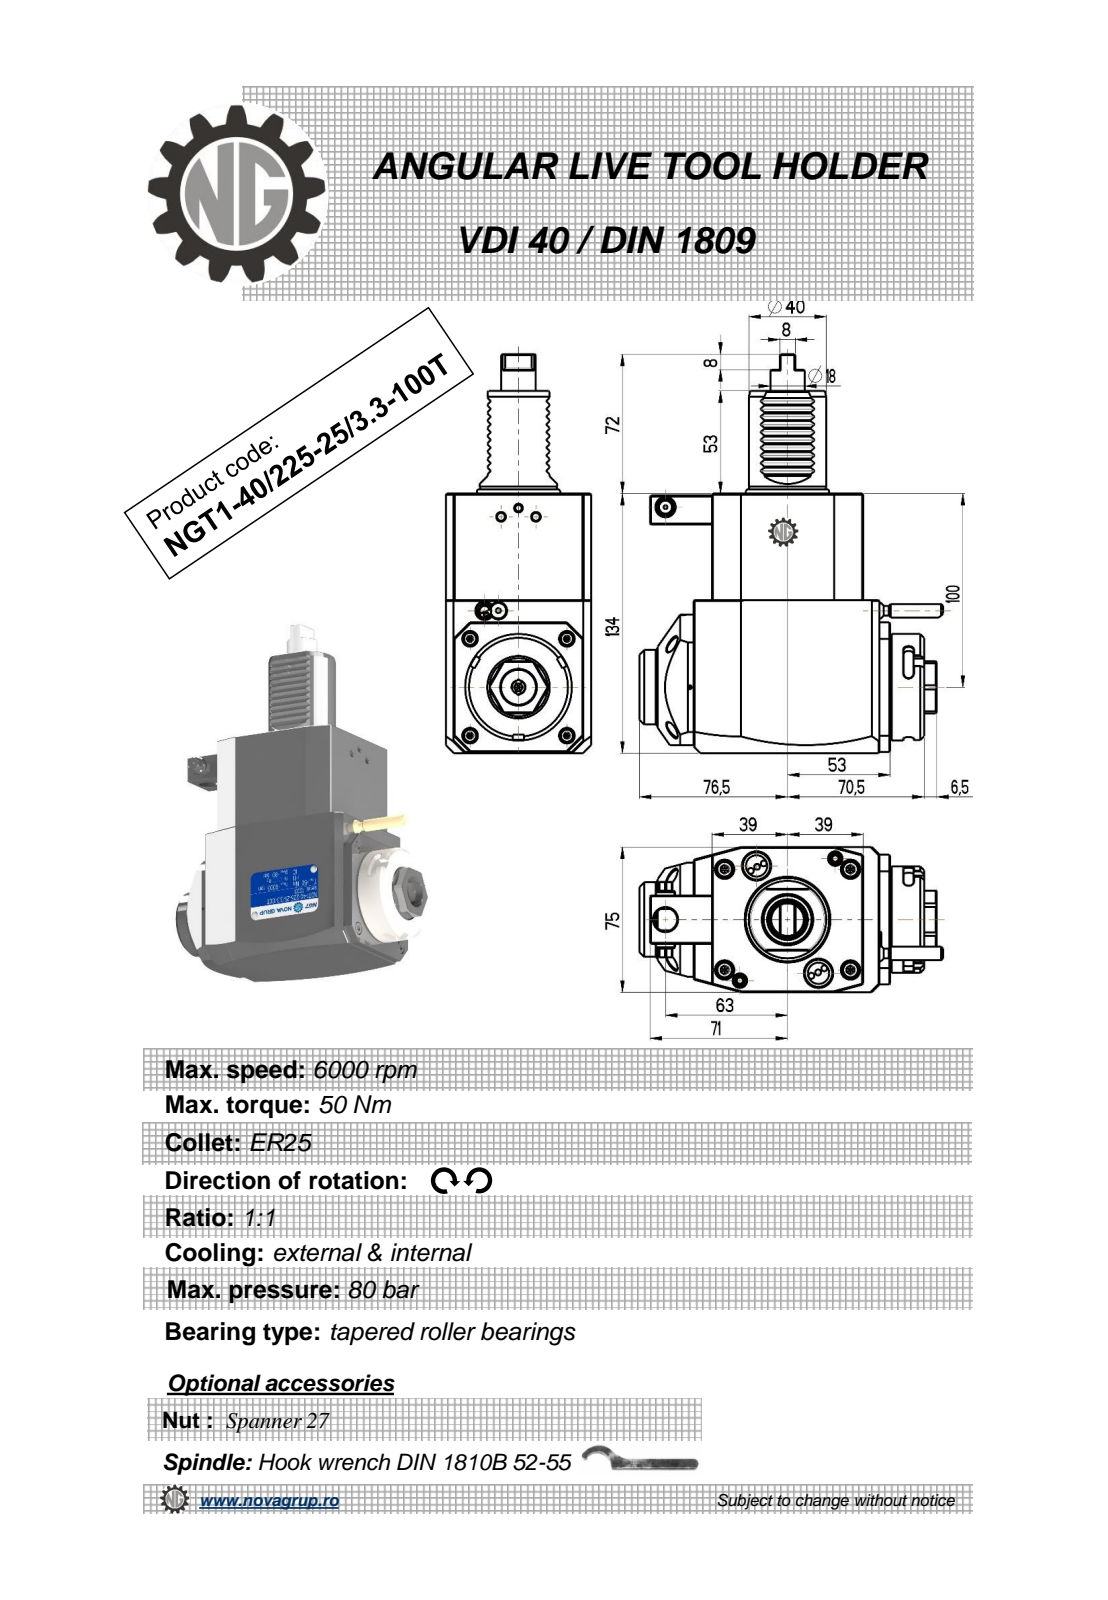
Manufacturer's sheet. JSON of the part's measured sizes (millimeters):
{"part_name": "NGT1_40_225_25_3_3_100T", "step_written_by": "PRO/ENGINEER BY PARAMETRIC TECHNOLOGY CORPORATION, 2010280 (CONFIG_CONTROL_DESIGN)", "units": "millimeters", "bodies": {"solids": 1, "faces": 392, "planar": 217, "cylindrical": 97, "other": 78}, "overall_size": [206, 156.83, 75], "volume_mm3": 1071000, "surface_area_mm2": 77452, "round_holes": [[2, 1], [2.5, 1], [3, 1], [9.5, 1], [12, 1], [18, 1]], "round_bosses_or_shafts": [[8, 2], [55, 1], [48, 1], [40, 1], [38.5, 1], [17.8, 1], [10, 1], [7, 1]], "partial_cylinders_radius": [[0.3, 20], [2.5, 6], [0.8, 2], [180, 2], [3.85, 1], [4.25, 1], [15, 1], [24.5, 1]], "face_to_face_distances": [75, 134, 78, 14, 92, 17.5, 31.5, 84.88, 109.5, 54], "hole_center_spacings": [43.2, 55.81, 92.5]}
